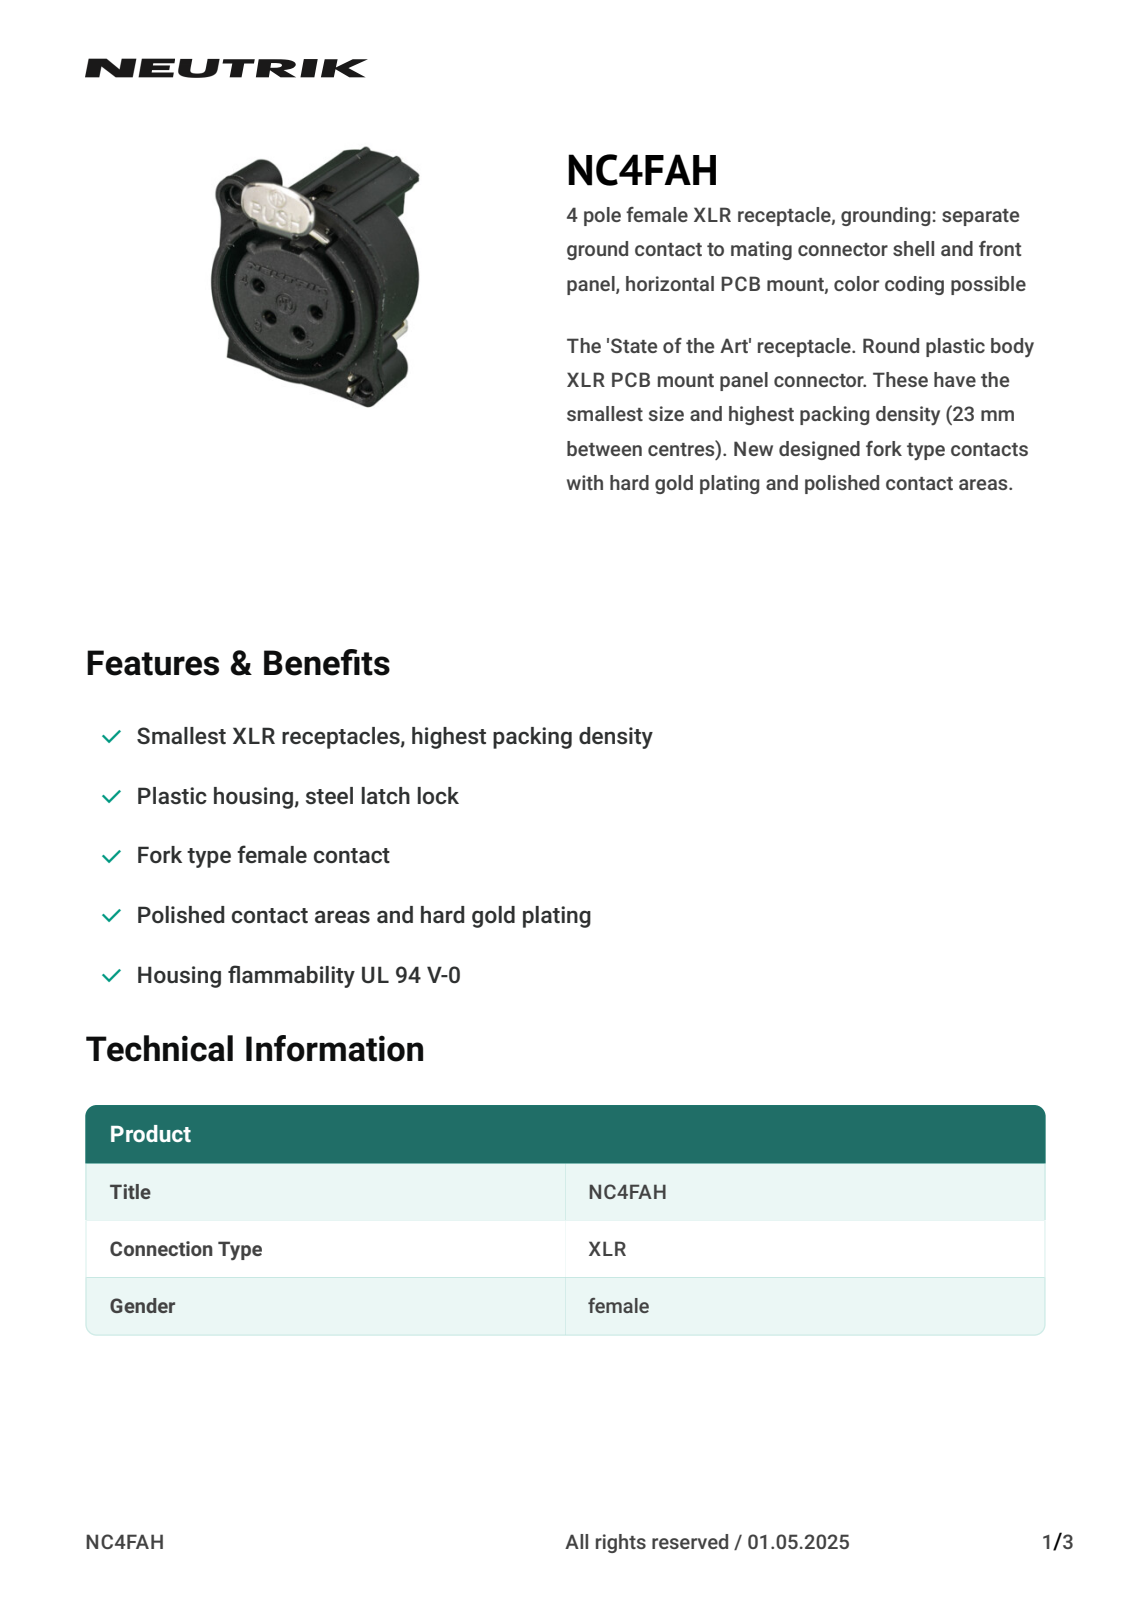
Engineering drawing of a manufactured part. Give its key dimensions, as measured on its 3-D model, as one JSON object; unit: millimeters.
{"part_name": "NC4FAH-0", "step_written_by": "CREO PARAMETRIC BY PTC INC, 2021184 (CONFIG_CONTROL_DESIGN)", "units": "millimeters", "bodies": {"solids": 2, "faces": 1740, "planar": 1209, "cylindrical": 355, "other": 176}, "overall_size": [32.65, 26.1, 25], "volume_mm3": 6271, "surface_area_mm2": 6858, "round_holes": [[1.7, 4], [1.37, 2], [2.35, 2], [2.5, 1], [2.51, 1], [3, 1], [19.5, 1], [20.55, 1]], "round_bosses_or_shafts": [[1.5, 2], [22, 1], [20.5, 1], [15.8, 1], [5.2, 1], [3, 1], [2.19, 1]], "partial_cylinders_radius": [[0.2, 119], [0.5, 28], [0.12, 9], [1, 9], [0.4, 6], [0.7, 5], [2, 5], [0.25, 4]], "face_to_face_distances": [11.8, 0.5, 1, 8.3, 2, 4.7, 0.94, 2.7, 13, 5.6], "hole_center_spacings": [3.22, 4.27, 11.62, 14, 25.53, 3.55, 4.19, 4.2]}
